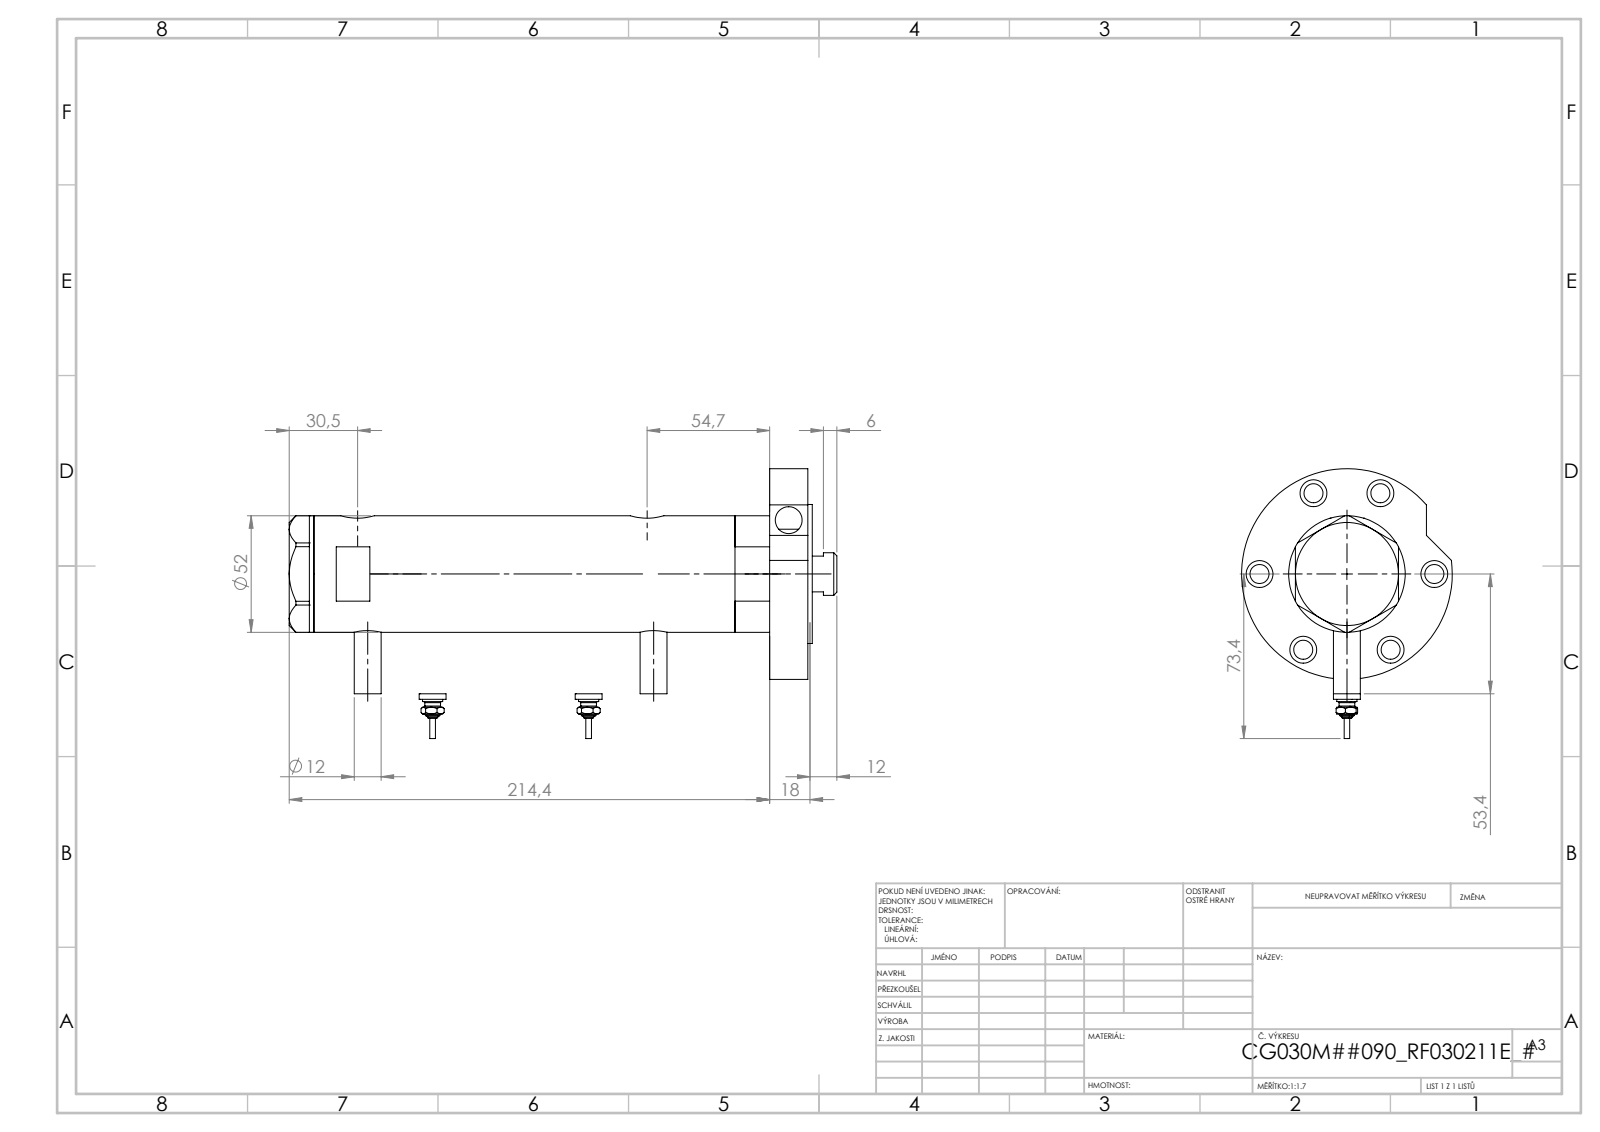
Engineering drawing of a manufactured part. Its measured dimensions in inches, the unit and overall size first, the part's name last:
Units: inches
Overall size (bounding box): 9.41 × 4.146 × 3.701
Round holes (diameter × count): ⌀0.472 ×7, ⌀0.335 ×6, ⌀0.197 ×2, ⌀0.383 ×2, ⌀0.492 ×2, ⌀0.591 ×2, ⌀0.256 ×1, ⌀0.787 ×1, ⌀0.846 ×1, ⌀1.181 ×1, ⌀1.299 ×1, ⌀1.575 ×1
Round bosses / shafts (diameter × count): ⌀0.472 ×2, ⌀0.354 ×2, ⌀0.276 ×2, ⌀0.197 ×2, ⌀0.171 ×2, ⌀0.094 ×2, ⌀3.701 ×1, ⌀2.441 ×1
Main face-to-face distances: 0.669, 7.694, 8.364, 2.043, 0.079, 8.443, 5.651, 2.713, 2.791, 0.748
Hole centre spacings: 1.535, 0.114, 0.177, 1.706, 2.553, 2.659, 2.754, 3.064
Volume: 31 in³ · Surface area: 185.5 in²
Bodies: 7 solids, 290 faces (106 planar, 110 cylindrical, 74 other)
Part name (STEP PRODUCT): V270CG_FRONT; V270CG_BACK; V270CG_SWITCH; V270CG_VC (+2 more)
STEP written by: SolidWorks 2019 (CONFIG_CONTROL_DESIGN)
